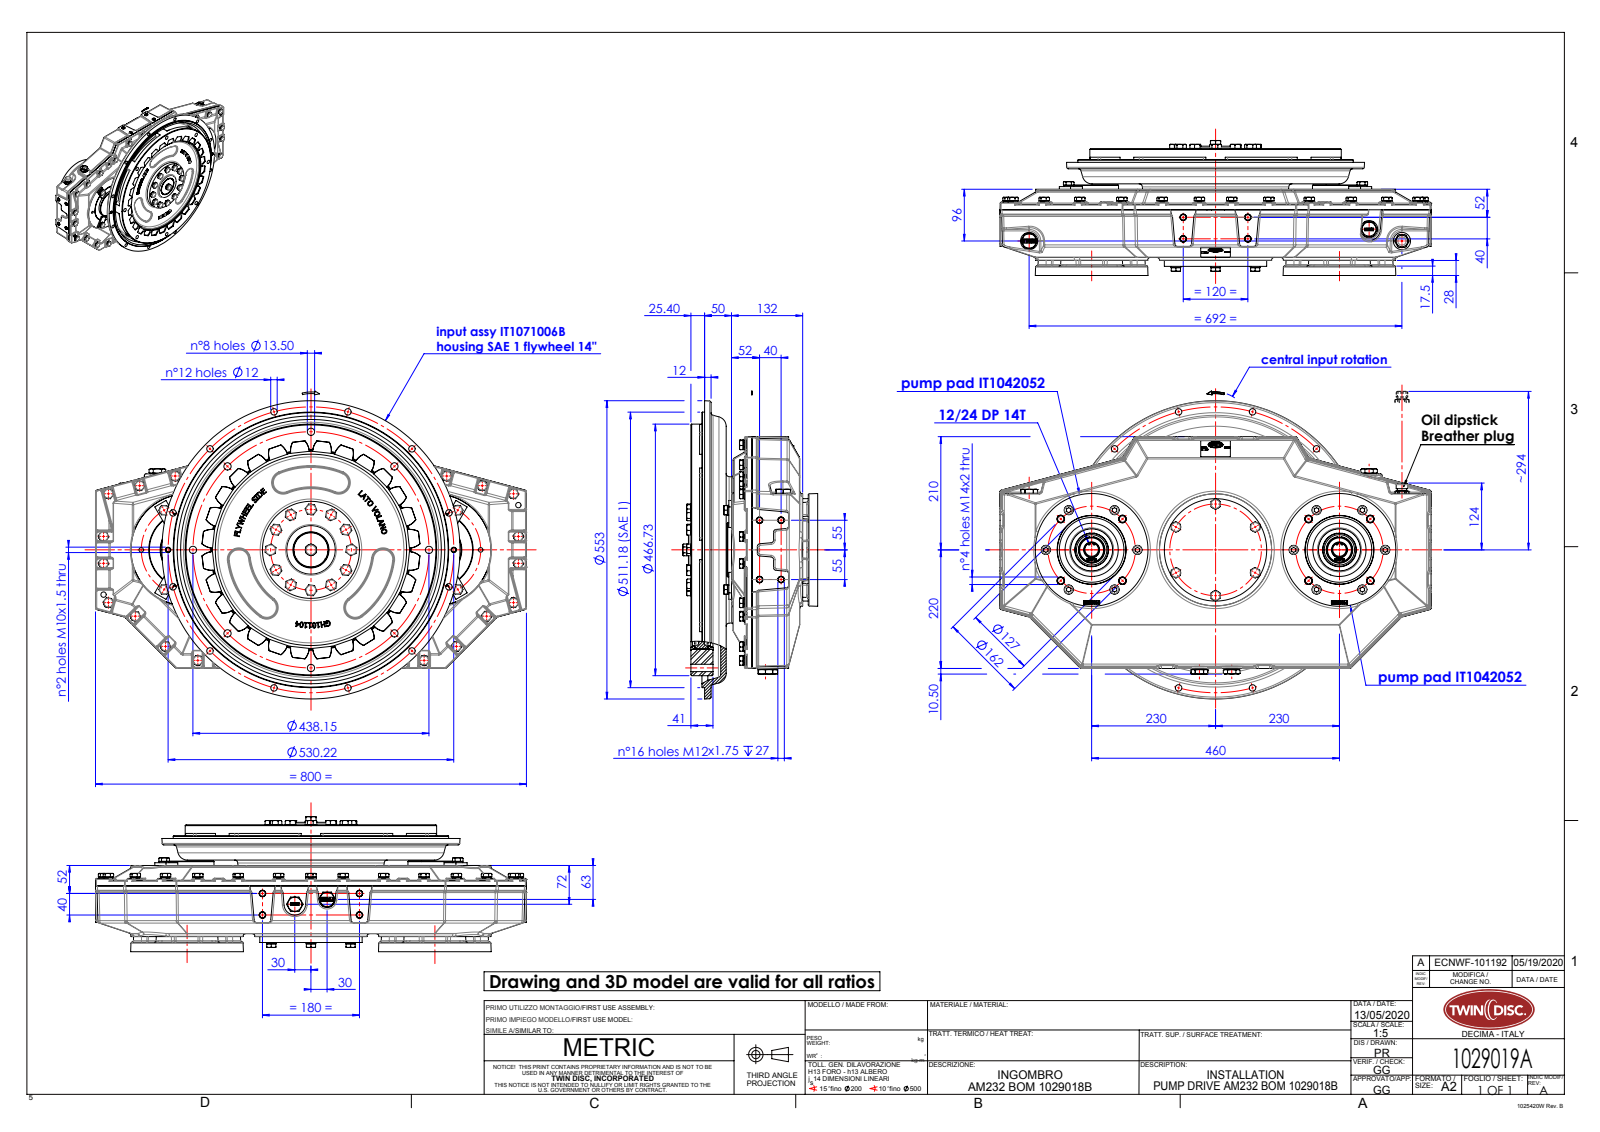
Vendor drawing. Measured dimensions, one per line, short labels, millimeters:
name: IT1042052_rev00-installation; IT0000203_rev00-installation; IT4588040_rev00-installation; ITam232-012_rev00-installation (+6 more)
written by: SolidWorks 2007 (AUTOMOTIVE_DESIGN)
unit: mm
bodies: 48 solids, 10291 faces (3978 planar, 3299 cylindrical, 3014 other)
size: 800 × 564.17 × 250.5
volume: 9 922 000 mm³; area: 3 936 000 mm²
holes: 58× ⌀10.2, 32× ⌀8.5, 32× ⌀12, 29× ⌀10.5, 20× ⌀13, 18× ⌀11, 12× ⌀17, 10× ⌀10, 8× ⌀13.5, 8× ⌀14, 7× ⌀12.2, 4× ⌀2
bosses: 49× ⌀10, 39× ⌀18.1, 39× ⌀16.2, 19× ⌀18, 19× ⌀12, 12× ⌀24, 12× ⌀16, 7× ⌀21.1
rounds: 284× R2, 112× R0.75, 112× R5, 80× R3, 76× R2.5, 58× R0.45, 56× R34, 56× R34.2
face distances: 10, 38, 58, 48, 20, 50.9, 132, 28, 40.9, 126.5
hole spacings: 120, 57.4, 75, 138.58, 40, 150, 207.84, 30
